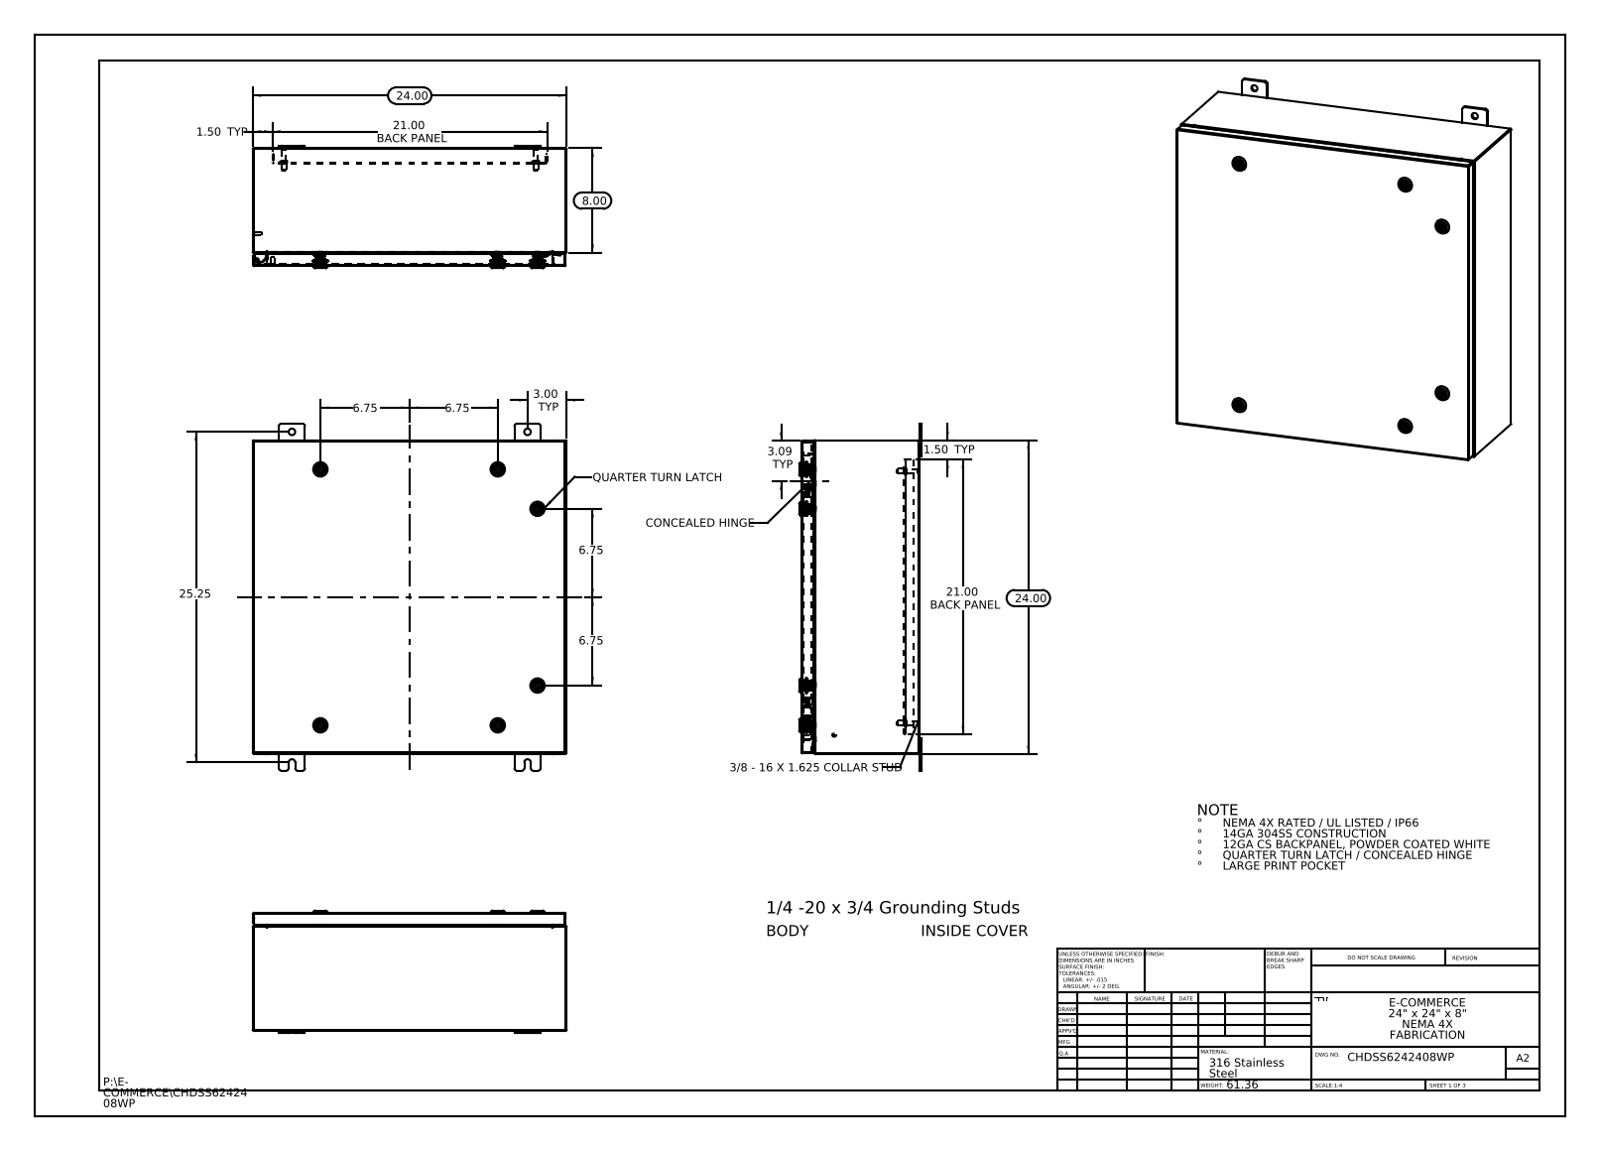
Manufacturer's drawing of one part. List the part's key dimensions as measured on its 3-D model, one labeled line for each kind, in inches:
Part name (STEP PRODUCT): CHDSS6242408WP Mounting Feet; Nut-211301-IB-Industrilas_Nut-211301-IB-Industrilas; Concealed Hinge (Cover Side); Quarter-20 CD Stud (+8 more)
STEP written by: SolidWorks 2013 (CONFIG_CONTROL_DESIGN)
Units: inches
Bodies: 55 solids, 5420 faces (1592 planar, 1692 cylindrical, 2136 other)
Overall size (bounding box): 26.5 × 24 × 9.356
Volume: 218.6 in³ · Surface area: 5 453 in²
Round holes (diameter × count): ⌀0.5 ×8, ⌀0.197 ×6, ⌀0.394 ×6, ⌀0.4 ×6, ⌀0.63 ×6, ⌀0.787 ×6, ⌀0.136 ×4, ⌀0.211 ×1
Round bosses / shafts (diameter × count): ⌀0.236 ×8, ⌀1.102 ×6, ⌀0.78 ×6, ⌀0.626 ×6, ⌀0.61 ×6, ⌀0.531 ×6, ⌀0.392 ×6, ⌀0.114 ×6
Partial cylindrical surfaces — rounded edges, fillets, slot ends (radius × count): R0.006 ×198, R0.118 ×198, R0.028 ×72, R0.02 ×24, R0.19 ×24, R0.197 ×24, R0.013 ×20, R0.088 ×18
Main face-to-face distances: 0.075, 23.925, 0.074, 9.01, 8.935, 8.936, 8.861, 0.104, 1, 1.075
Hole centre spacings: 0.688, 1.858, 2.878, 3.065, 13.55, 16.376, 17.687, 18
